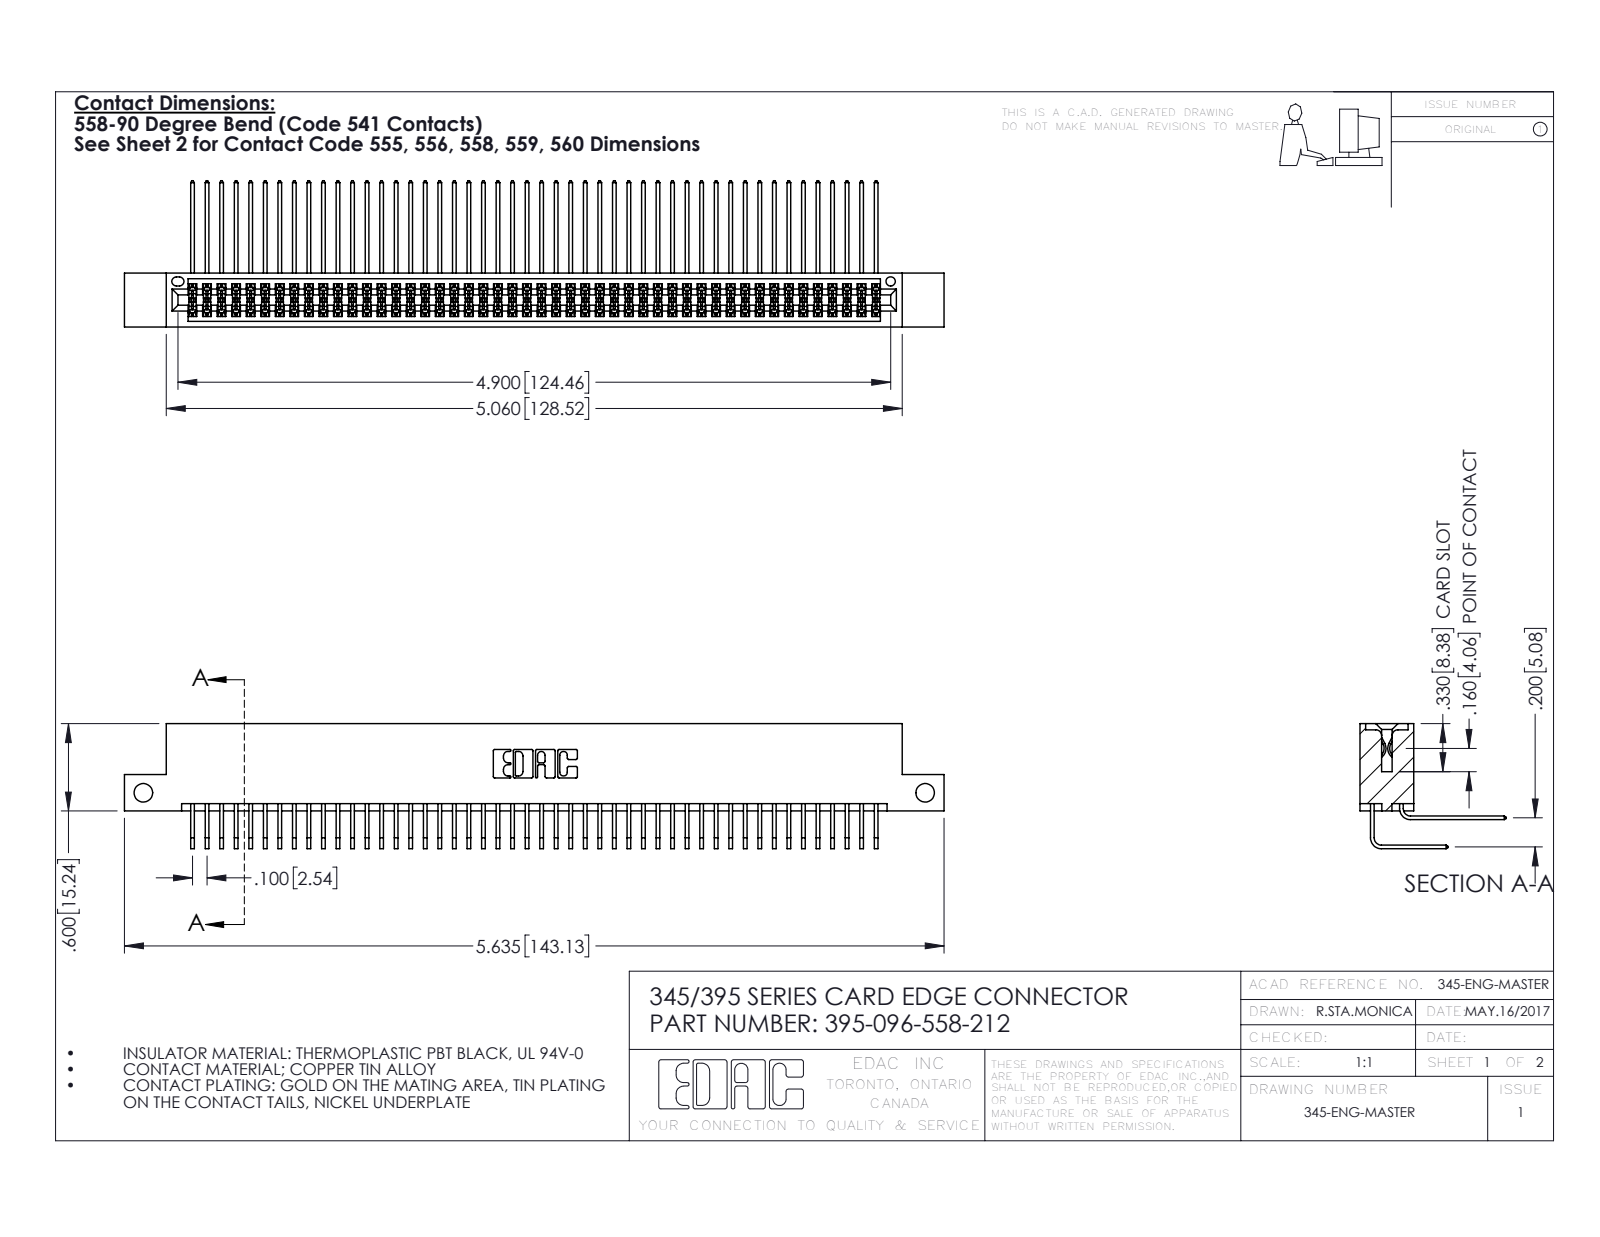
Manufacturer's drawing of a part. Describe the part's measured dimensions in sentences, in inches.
The part is named "345-292-001_558 Tail - 2; 395-096-558-212; 345-292-001_558 559 Tail - 1; 345 Part_Flush Mounting Lugs - Side Mount". Its 3-D file was written by "SolidWorks 2016 (CONFIG_CONTROL_DESIGN)". It is 97 solids with 5118 faces: 3440 planar, 1678 cylindrical and 0 other. Overall it measures 5.635 by 1.005 by 0.859 inches. Its volume is 0.88 cubic inches and its surface area 37.06 square inches. Round holes: 2 of diameter 0.128, 1 of diameter 0.064. Partial cylindrical surfaces (rounded edges, fillets, slot ends): 145 of radius 0.006, 22 of radius 0.01, 6 of radius 0.007, 6 of radius 0.031, 3 of radius 0.026, 2 of radius 0.014, 2 of radius 0.019, 2 of radius 0.022. The main face-to-face distances are 0.072, 0.298, 0.2, 0.37, 0.098, 0.272, 0.025, 0.225, 0.025, 0.175. The hole center spacings are 5.375.
